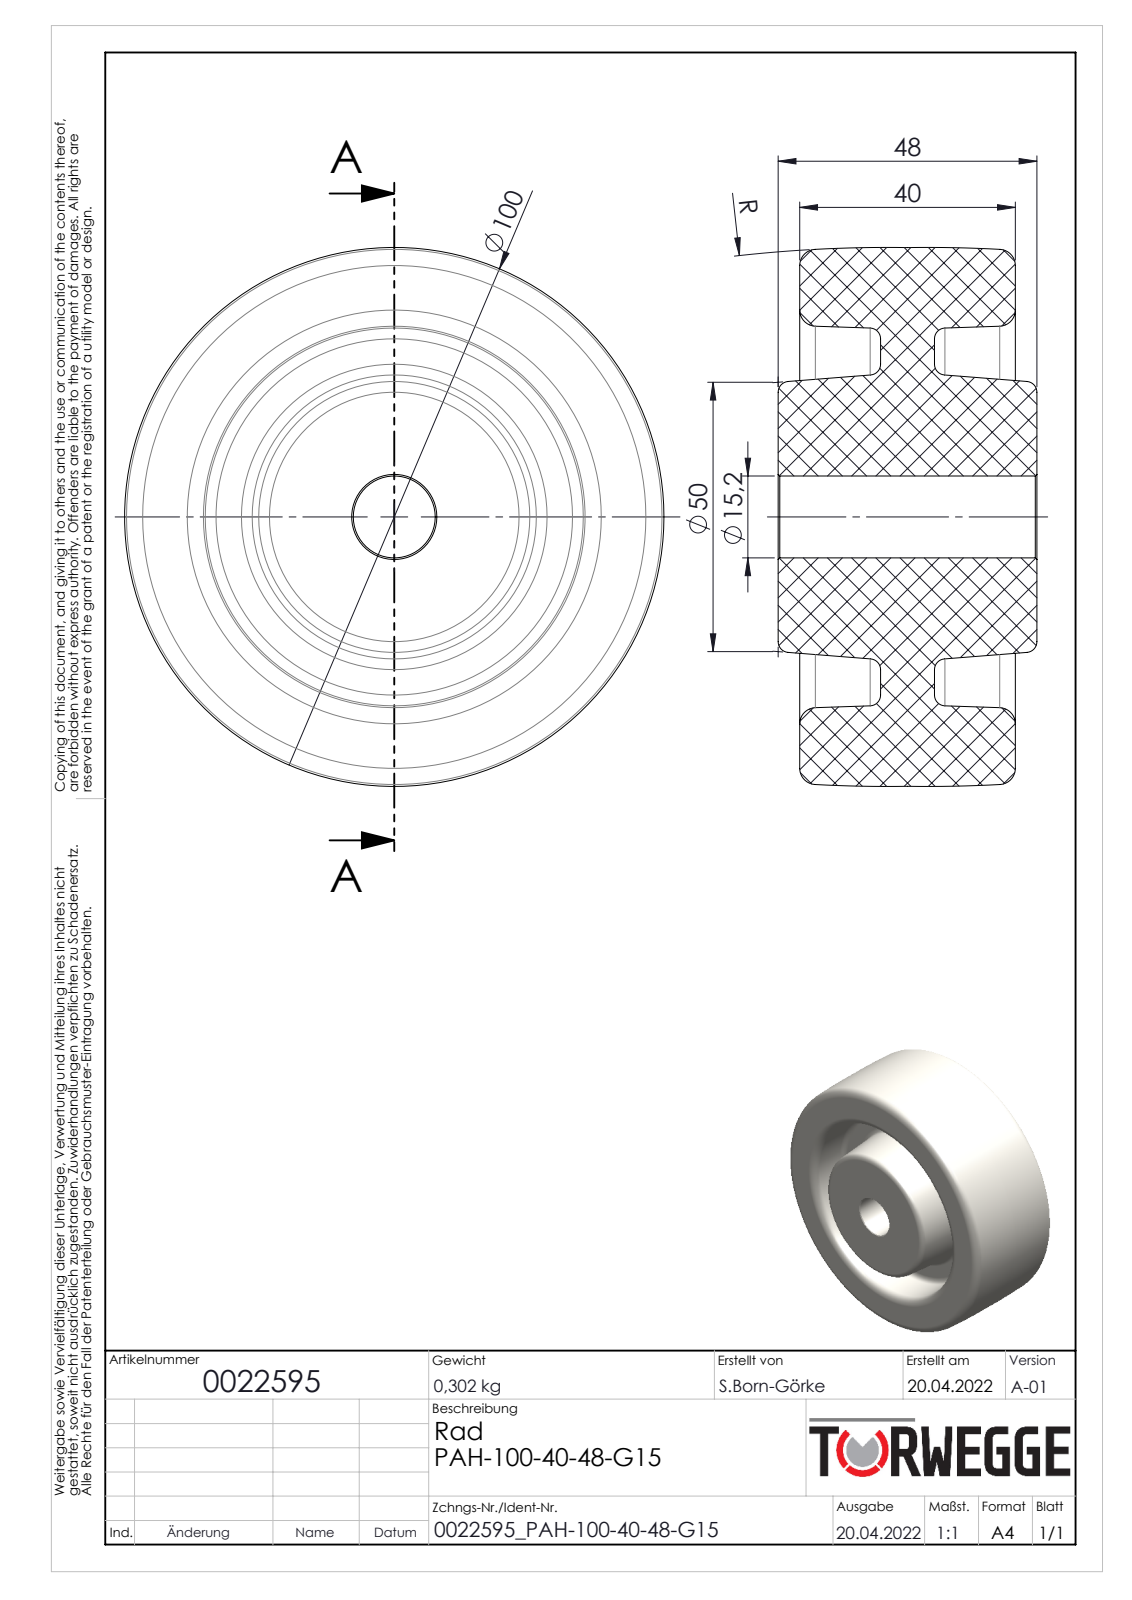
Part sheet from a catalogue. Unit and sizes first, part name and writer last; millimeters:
Units: millimetres
Overall size (bounding box): 100.06 × 100.06 × 48
Round holes (diameter × count): ⌀15.2 ×1
Main face-to-face distances: 4, 44, 40, 19, 29, 15, 25, 48, 10
Volume: 264 572 mm³ · Surface area: 39 919 mm²
Bodies: 1 solid, 44 faces (6 planar, 2 cylindrical, 36 other)
Part name (STEP PRODUCT): 0022595
STEP written by: SolidWorks 2020 (AUTOMOTIVE_DESIGN)
